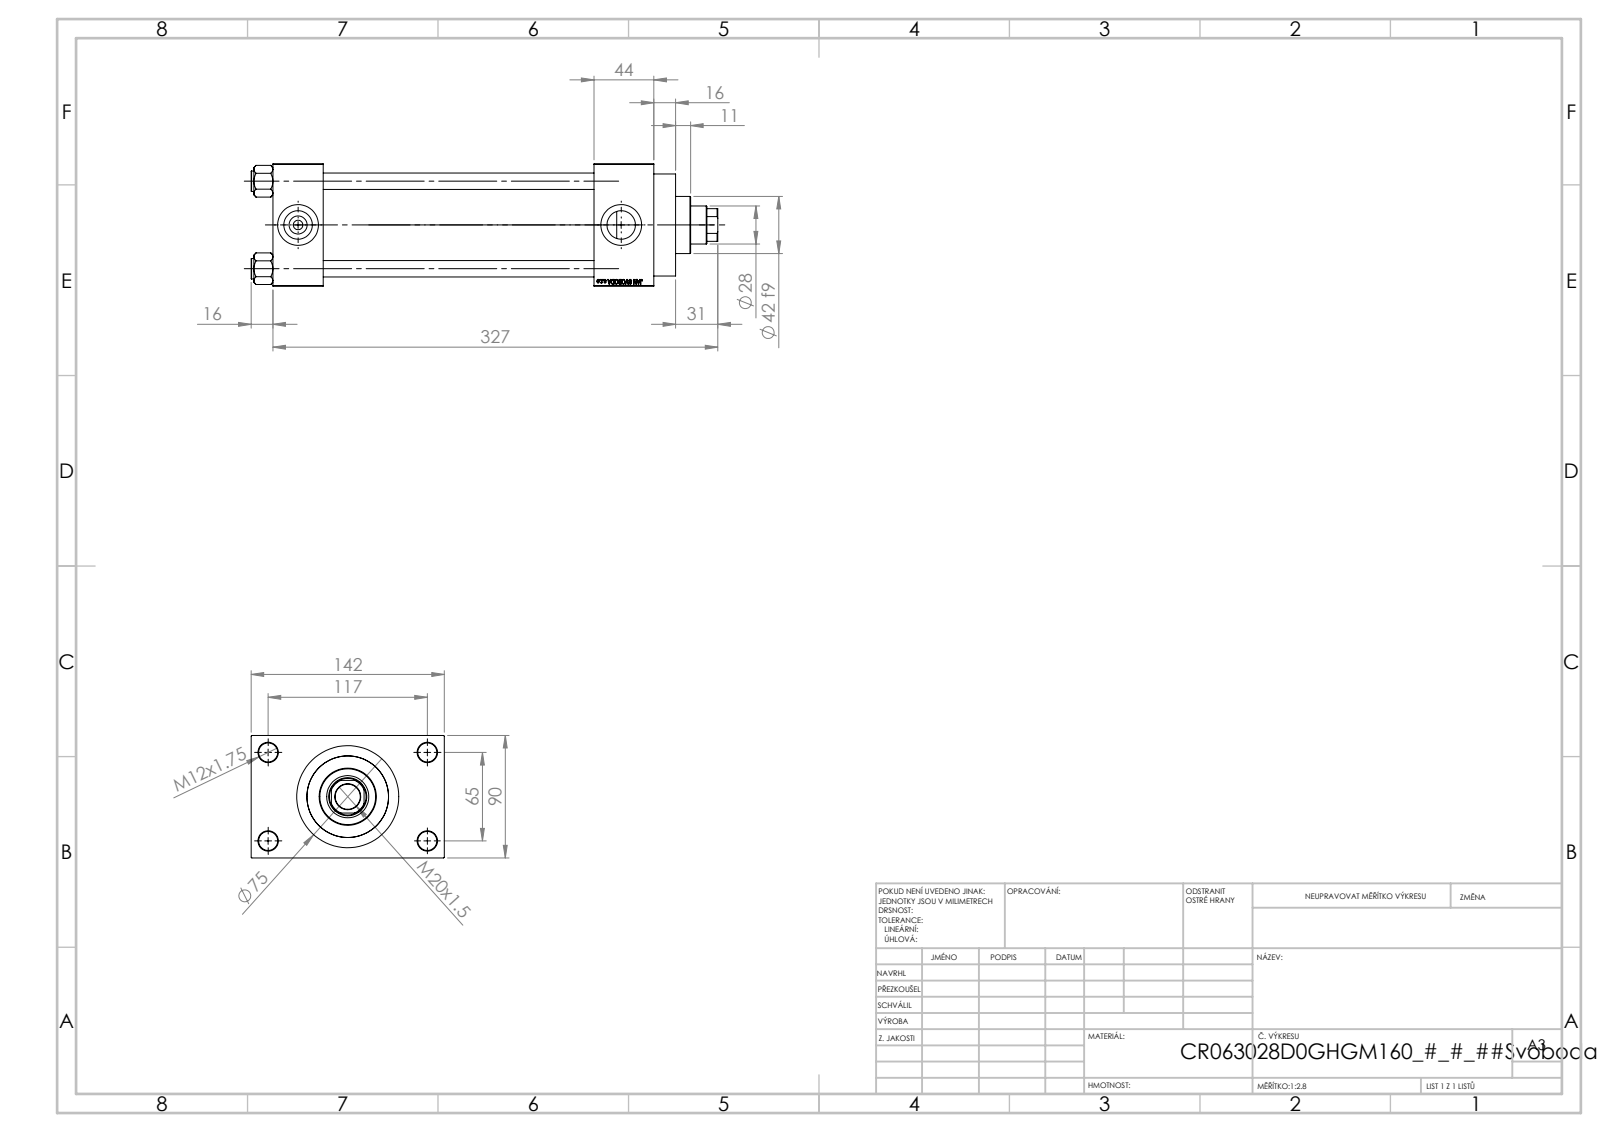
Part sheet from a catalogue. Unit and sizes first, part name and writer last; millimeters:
Units: millimetres
Overall size (bounding box): 343 × 142 × 90
Round holes (diameter × count): ⌀12 ×4, ⌀14 ×4, ⌀7 ×2, ⌀20.96 ×2, ⌀30 ×2, ⌀18.5 ×1, ⌀28 ×1, ⌀31 ×1, ⌀50 ×1, ⌀60 ×1, ⌀63 ×1
Round bosses / shafts (diameter × count): ⌀15 ×4, ⌀75 ×1, ⌀69 ×1, ⌀42 ×1
Partial cylindrical surfaces — rounded edges, fillets, slot ends (radius × count): R13.5 ×1
Main face-to-face distances: 90, 199, 37, 236, 243, 280, 44, 26, 116, 16
Hole centre spacings: 26.35, 45.47, 64.3, 66.92, 69.81, 90.65, 111.34, 65
Volume: 1 333 000 mm³ · Surface area: 291 797 mm²
Bodies: 11 solids, 1103 faces (497 planar, 88 cylindrical, 518 other)
Part name (STEP PRODUCT): NUT_M5_D; V215_VC_A; V215CR_D_Body; V215CR_D_TYCINKA (+1 more)
STEP written by: SolidWorks 2019 (CONFIG_CONTROL_DESIGN)
